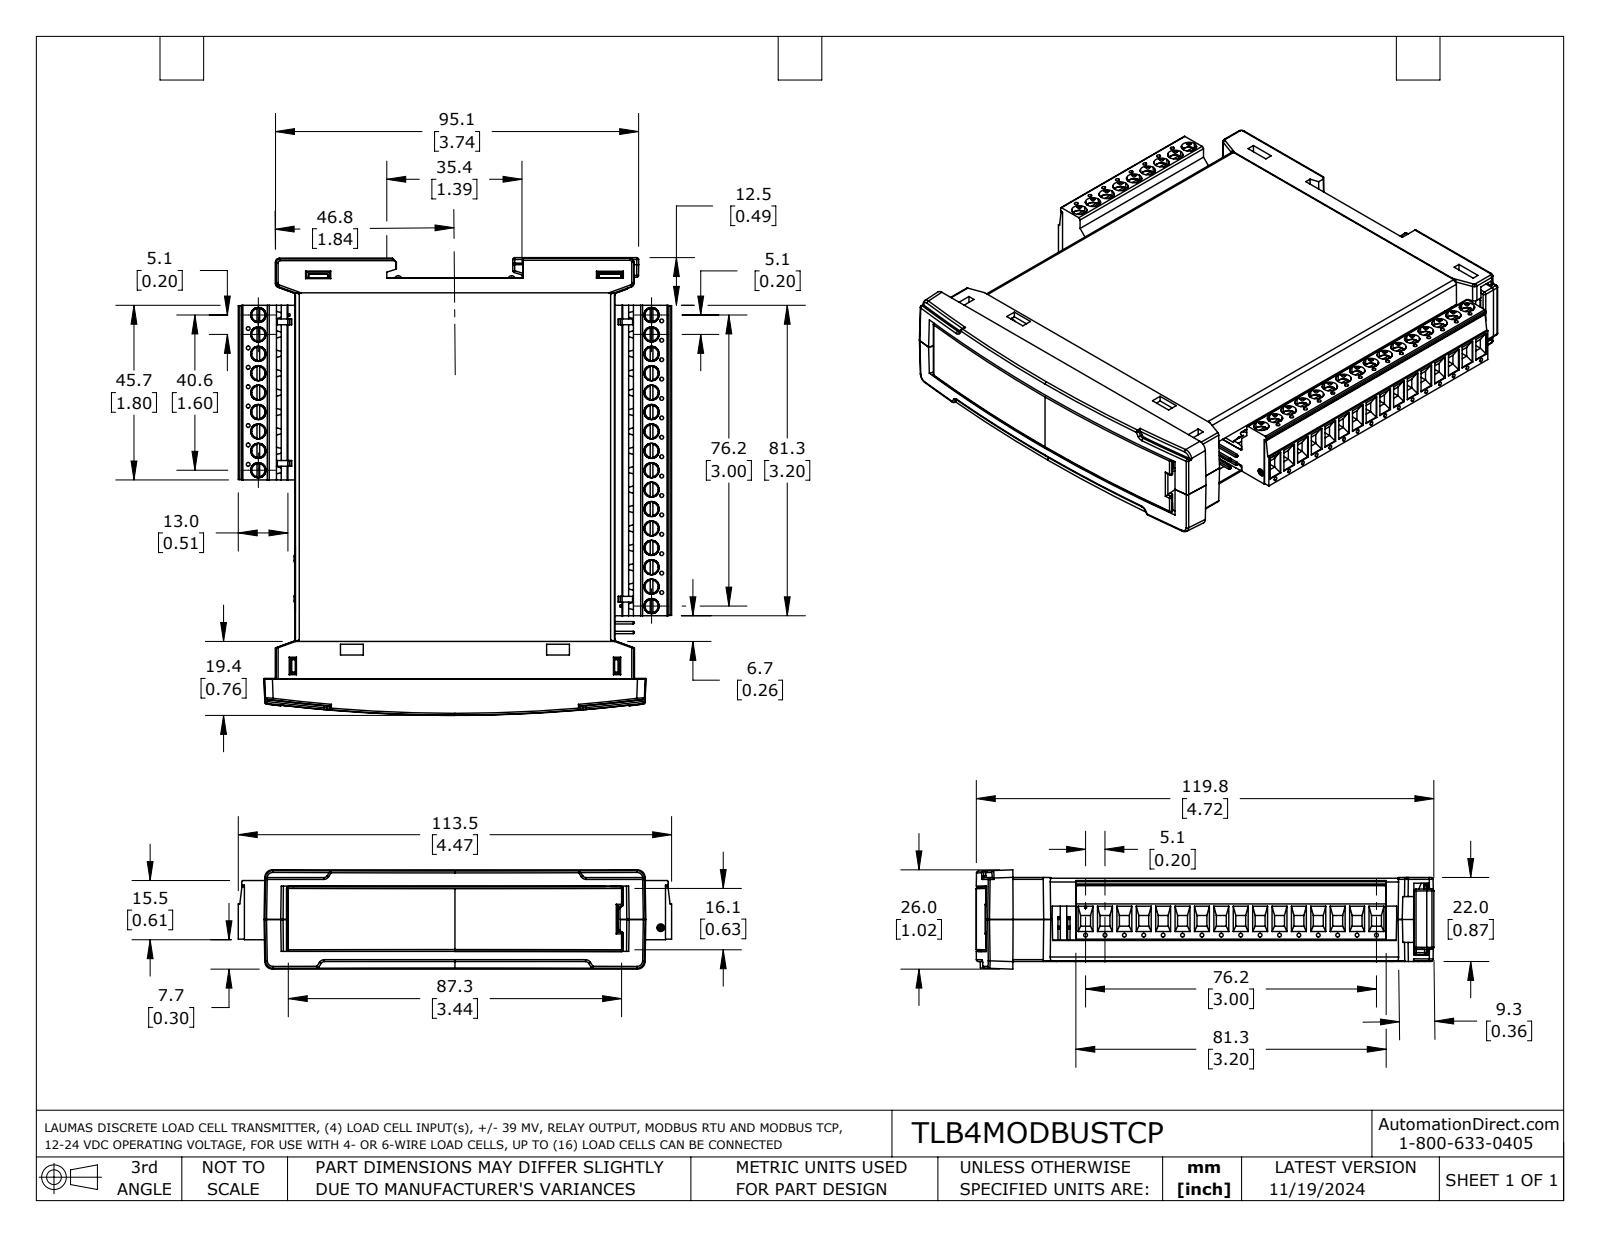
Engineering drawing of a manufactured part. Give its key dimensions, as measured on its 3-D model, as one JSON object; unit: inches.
{"part_name": "TLB4MODBUSTCP", "step_written_by": "SolidWorks 2021 (AUTOMOTIVE_DESIGN)", "units": "inches", "bodies": {"solids": 26, "faces": 6312, "planar": 4003, "cylindrical": 1674, "other": 635}, "overall_size": [4.719, 4.469, 1.023], "volume_in3": 5.296, "surface_area_in2": 172.4, "round_holes": [[0.039, 56], [0.157, 25], [0.059, 16], [0.146, 16], [0.079, 6], [0.029, 4], [0.035, 4], [0.067, 2]], "round_bosses_or_shafts": [[0.152, 25], [0.055, 25], [0.108, 16], [0.114, 4], [0.06, 2], [0.051, 2], [0.093, 1]], "partial_cylinders_radius": [[0.02, 157], [0.004, 109], [0.005, 64], [0.012, 33], [0.039, 30], [0.069, 16], [0.118, 16], [0.122, 16]], "face_to_face_distances": [0.051, 0.799, 0.161, 0.059, 0.587, 0.65, 0.748, 0.063, 0.098, 0.701], "hole_center_spacings": [0.2, 0.4, 0.8, 0.6, 0.6, 4.06, 4.075, 1]}
